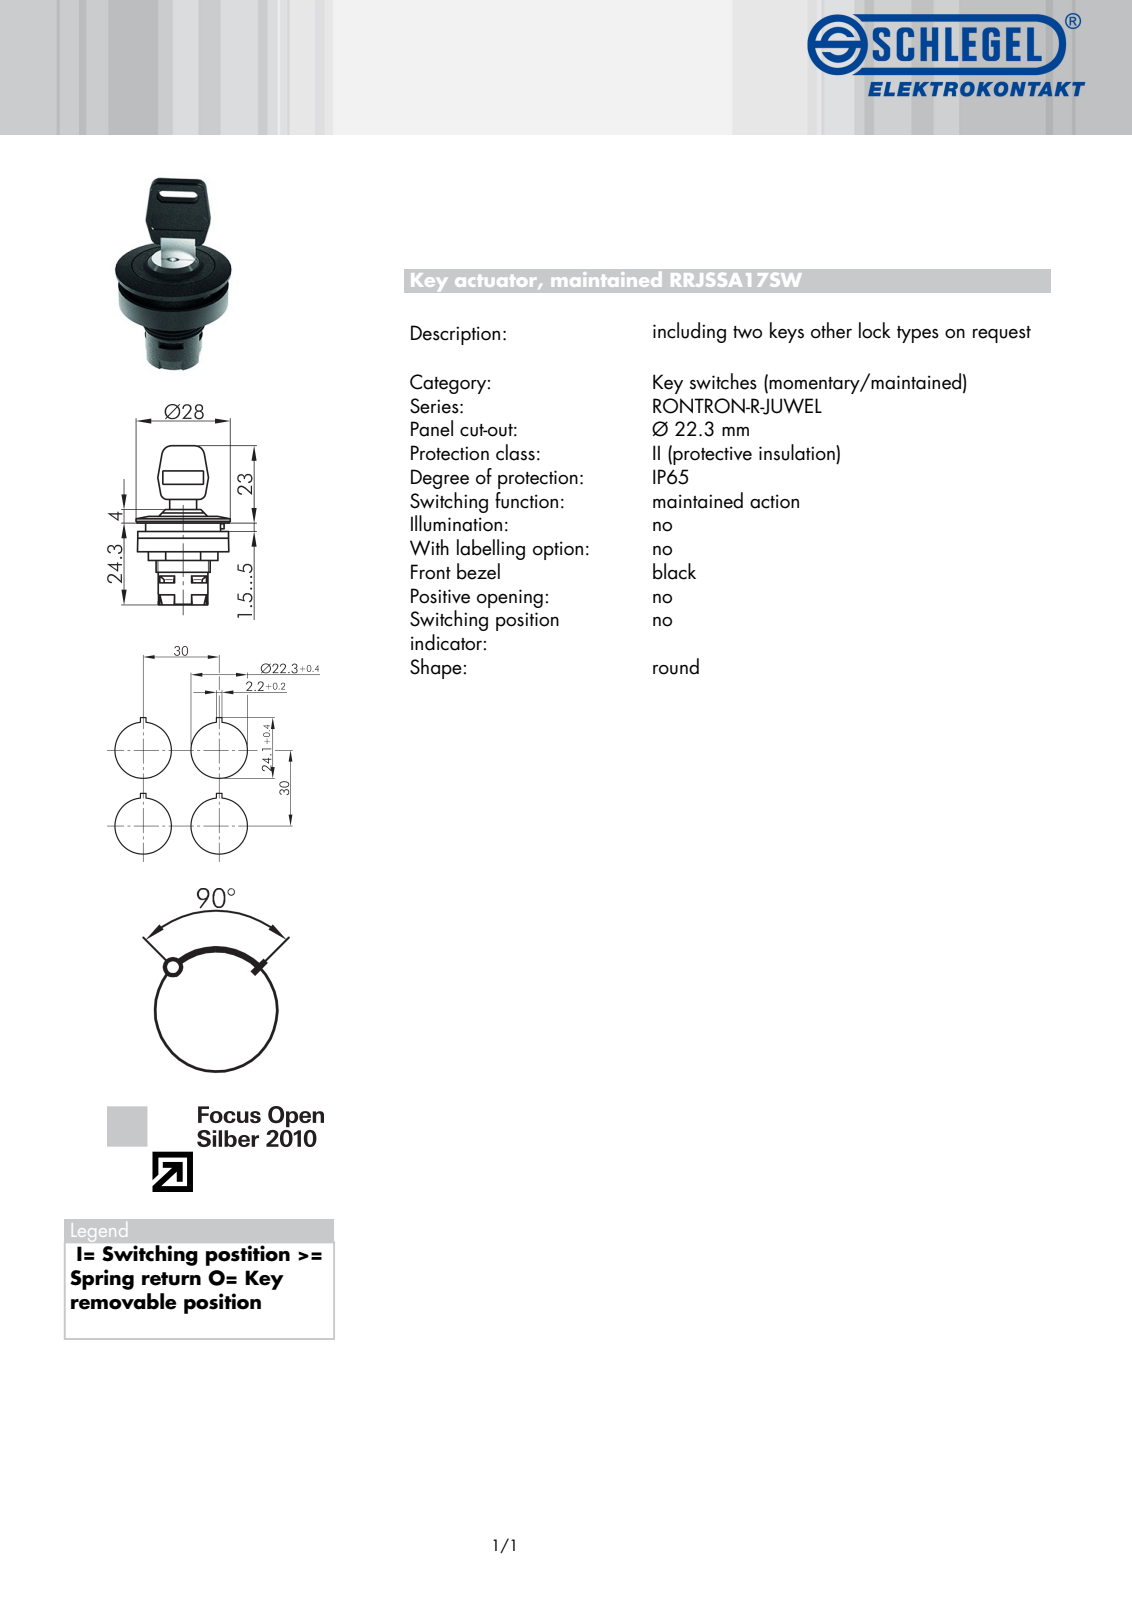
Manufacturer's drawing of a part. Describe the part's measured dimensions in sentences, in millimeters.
The part is named "RRJSSA17_ipt". Its 3-D file was written by "Autodesk Inventor 2014 (CONFIG_CONTROL_DESIGN)". It is 1 solid with 212 faces: 89 planar, 68 cylindrical and 55 other. Overall it measures 47.63 by 27.9 by 27.9 millimeters. Its volume is 8 615 cubic millimeters and its surface area 5 462 square millimeters. Round holes: 1 of diameter 12.65, 1 of diameter 14.92, 1 of diameter 16.5, 1 of diameter 20.05, 1 of diameter 25. Round bosses or shafts: 1 of diameter 27.9, 1 of diameter 27.4, 1 of diameter 26.86, 1 of diameter 22.2, 1 of diameter 19.67, 1 of diameter 16, 1 of diameter 14.7, 1 of diameter 12. Partial cylindrical surfaces (rounded edges, fillets, slot ends): 26 of radius 0.5, 6 of radius 0.25, 6 of radius 2, 2 of radius 1.25, 1 of radius 6.28, 1 of radius 12.1. The main face-to-face distances are 9, 7.4, 1.6, 2, 15.3, 16.9, 24.3, 18.9, 3.6, 5.4.
